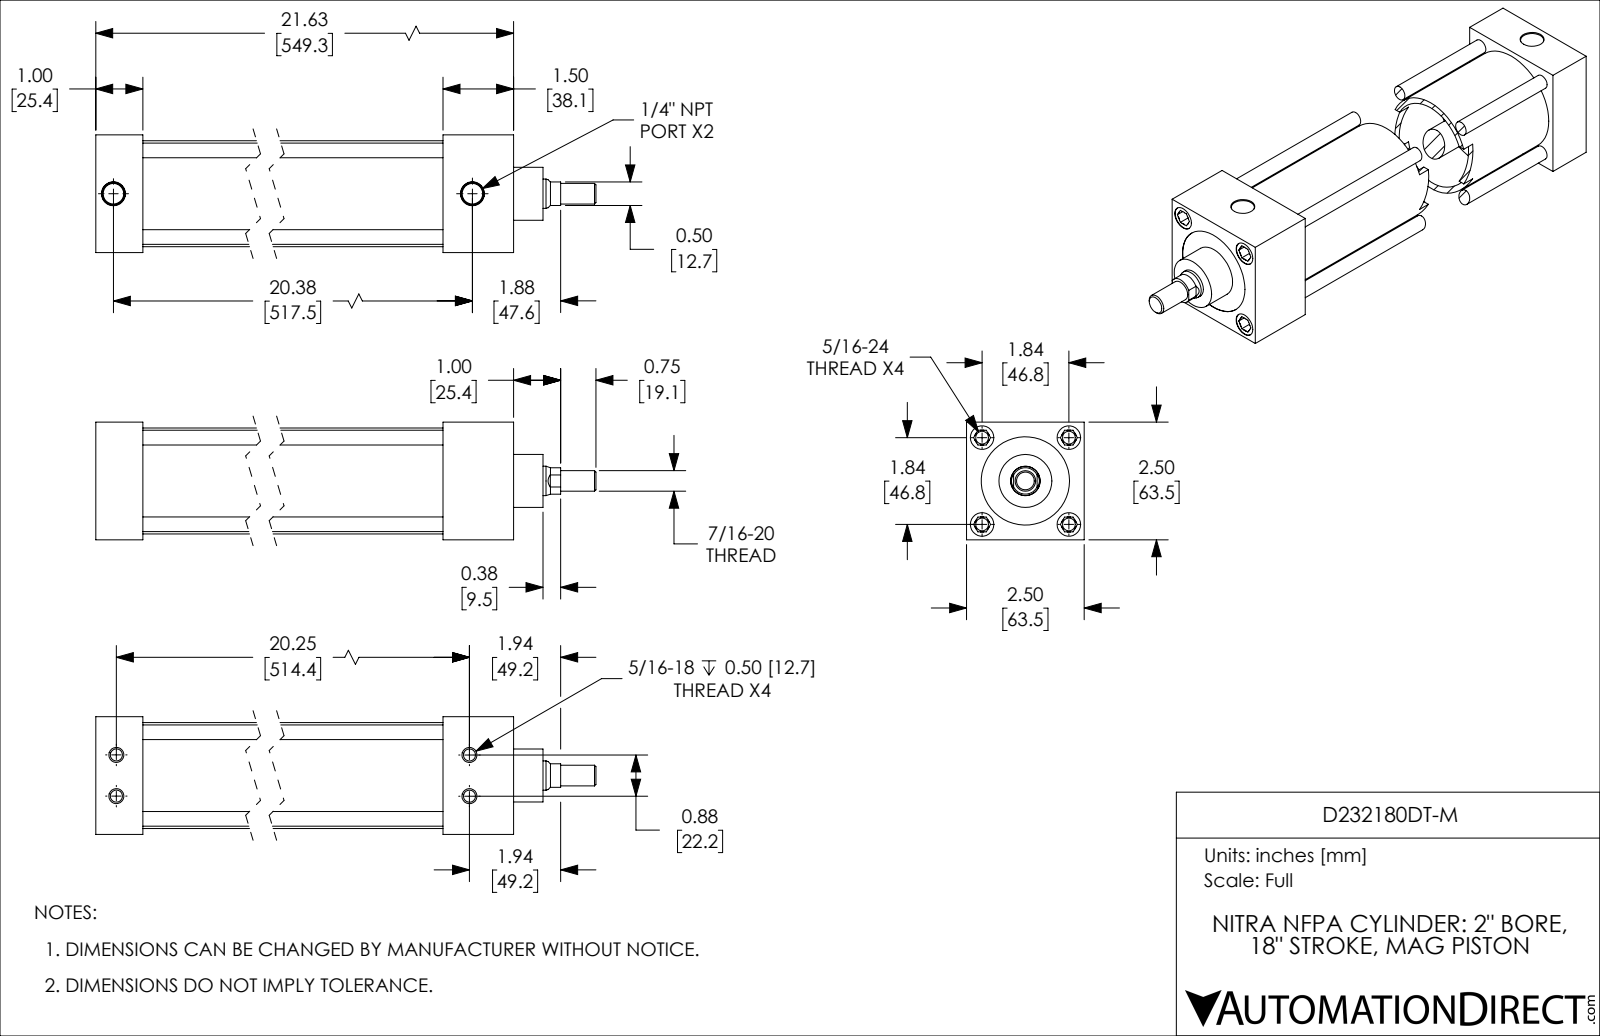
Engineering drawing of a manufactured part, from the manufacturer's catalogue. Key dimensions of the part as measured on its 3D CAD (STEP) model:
Part name (STEP PRODUCT): D232180DT-M_BODY; D232180DT-M; D232180DT-M_PISTON_KK1
STEP written by: SolidWorks 2019 (CONFIG_CONTROL_DESIGN)
Units: inches
Bodies: 2 solids, 200 faces (58 planar, 62 cylindrical, 80 other)
Overall size (bounding box): 23.375 × 2.5 × 2.5
Volume: 46.49 in³ · Surface area: 448.2 in²
Round holes (diameter × count): ⌀0.272 ×7, ⌀0.257 ×4, ⌀0.5 ×4, ⌀0.438 ×2, ⌀0.626 ×1, ⌀1.875 ×1, ⌀2.001 ×1
Round bosses / shafts (diameter × count): ⌀0.312 ×4, ⌀2.251 ×1, ⌀1.999 ×1, ⌀1.125 ×1, ⌀0.624 ×1, ⌀0.437 ×1
Partial cylindrical surfaces — rounded edges, fillets, slot ends (radius × count): R0.281 ×1
Main face-to-face distances: 2.5, 1, 20.125, 19.125, 2.125, 1.125, 18, 1.5, 21.625, 20.625
Hole centre spacings: 1.84, 1.844, 1.301, 0.441, 0.443, 0.875, 1.304, 2.602
